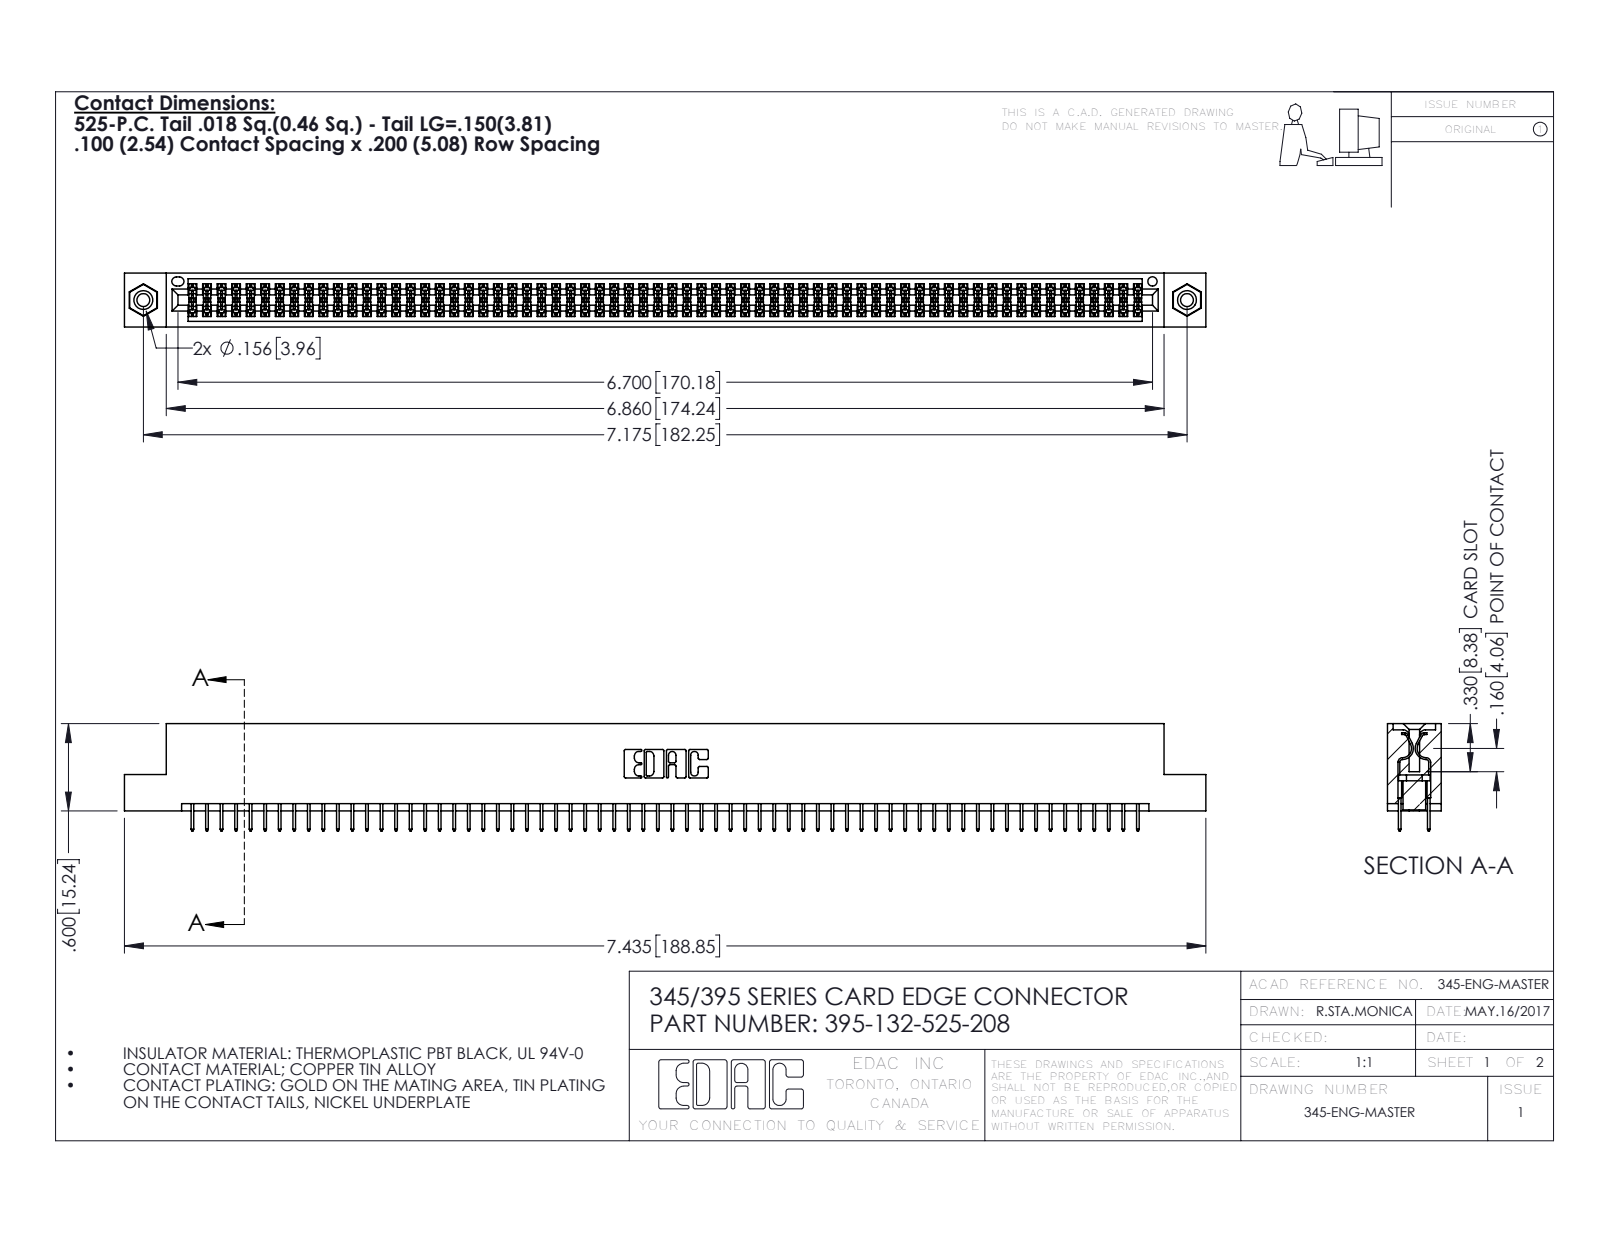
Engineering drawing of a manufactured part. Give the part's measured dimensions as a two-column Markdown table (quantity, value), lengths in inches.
| quantity | value |
| --- | --- |
| part name | 395-132-525-208; 345-250-001_345-250-003-102; 345-292-001_345-293-125; 345 Part_Flush Mounting Lugs - 0.156 Dia-TI |
| STEP written by | SolidWorks 2020 (CONFIG_CONTROL_DESIGN) |
| units | inches |
| bodies | 135 solids, 7314 faces (5260 planar, 2038 cylindrical, 16 other) |
| overall size | 7.435 × 0.737 × 0.37 |
| volume | 1.119 in³ |
| surface area | 41.76 in² |
| round holes (diameter × count) | 0.089 × 2, 0.125 × 2, 0.156 × 2, 0.064 × 1 |
| round bosses / shafts (diameter × count) | 0.155 × 2 |
| partial cylindrical surfaces (radius × count) | 0.006 × 198, 0.01 × 22, 0.007 × 6, 0.031 × 6, 0.026 × 3, 0.014 × 2, 0.019 × 2, 0.022 × 2 |
| main face-to-face distances | 0.072, 0.298, 0.2, 0.37, 0.098, 0.272, 0.025, 0.225, 0.072, 0.175 |
| hole center spacings | 0.27, 6.939, 7.175 |
